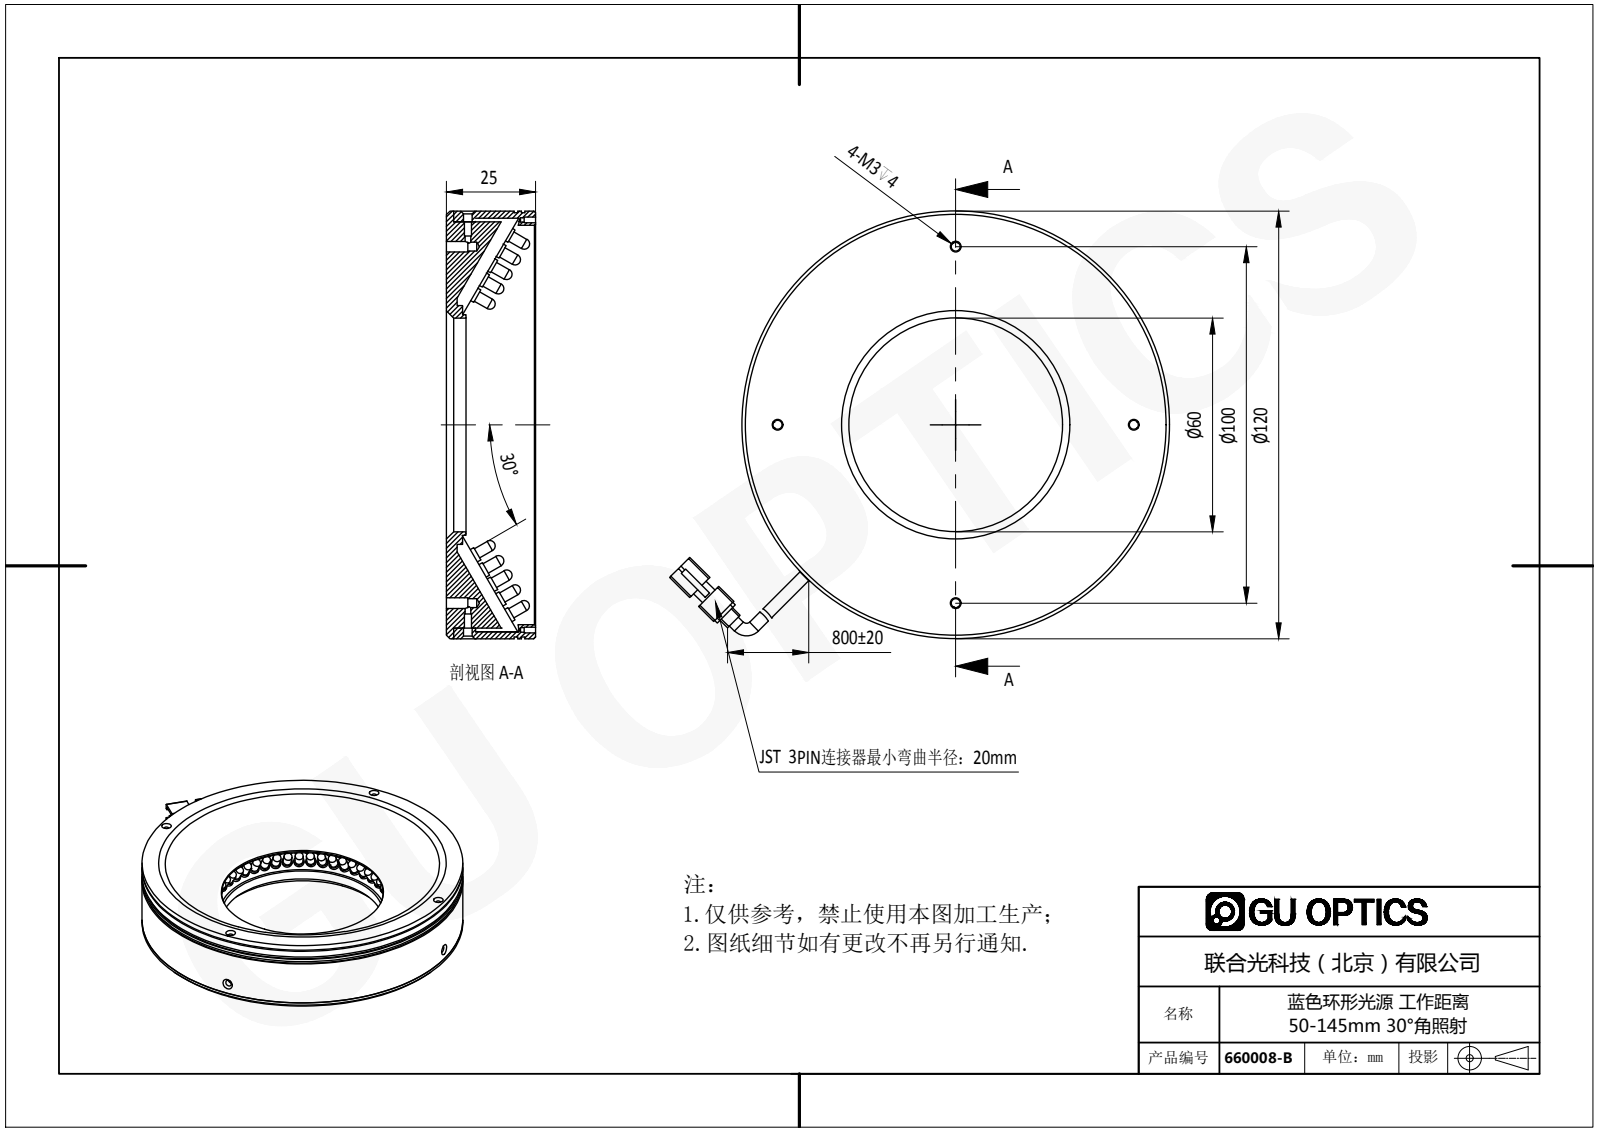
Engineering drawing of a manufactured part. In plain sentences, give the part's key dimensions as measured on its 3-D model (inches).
The part is named "660008-B". Its 3-D file was written by "SolidWorks 2016 (AUTOMOTIVE_DESIGN)". It is 321 solids with 5663 faces: 3870 planar, 1401 cylindrical and 392 other. Overall it measures 5.522 by 4.724 by 1.159 inches. Its volume is 7.516 cubic inches and its surface area 171.3 square inches. Round holes: 6 of diameter 0.063, 5 of diameter 0.138, 4 of diameter 0.049, 4 of diameter 0.067, 4 of diameter 0.098, 4 of diameter 0.118, 2 of diameter 0.079, 2 of diameter 0.094, 1 of diameter 2.362, 1 of diameter 4.409, 1 of diameter 4.567. Round bosses or shafts: 315 of diameter 0.15, 315 of diameter 0.118, 2 of diameter 0.138, 1 of diameter 4.724, 1 of diameter 4.685, 1 of diameter 4.488, 1 of diameter 2.638, 1 of diameter 2.435. Partial cylindrical surfaces (rounded edges, fillets, slot ends): 12 of radius 0.02, 4 of radius 0.039, 1 of radius 0.065, 1 of radius 0.315. The main face-to-face distances are 0.984, 0.079, 0.039, 0.906, 1.063, 0.02, 0.118, 0.098, 0.138, 0.793. The hole center spacings are 3, 0.295, 1.969, 2.264, 2.784, 3.202, 4.232, 0.205.
